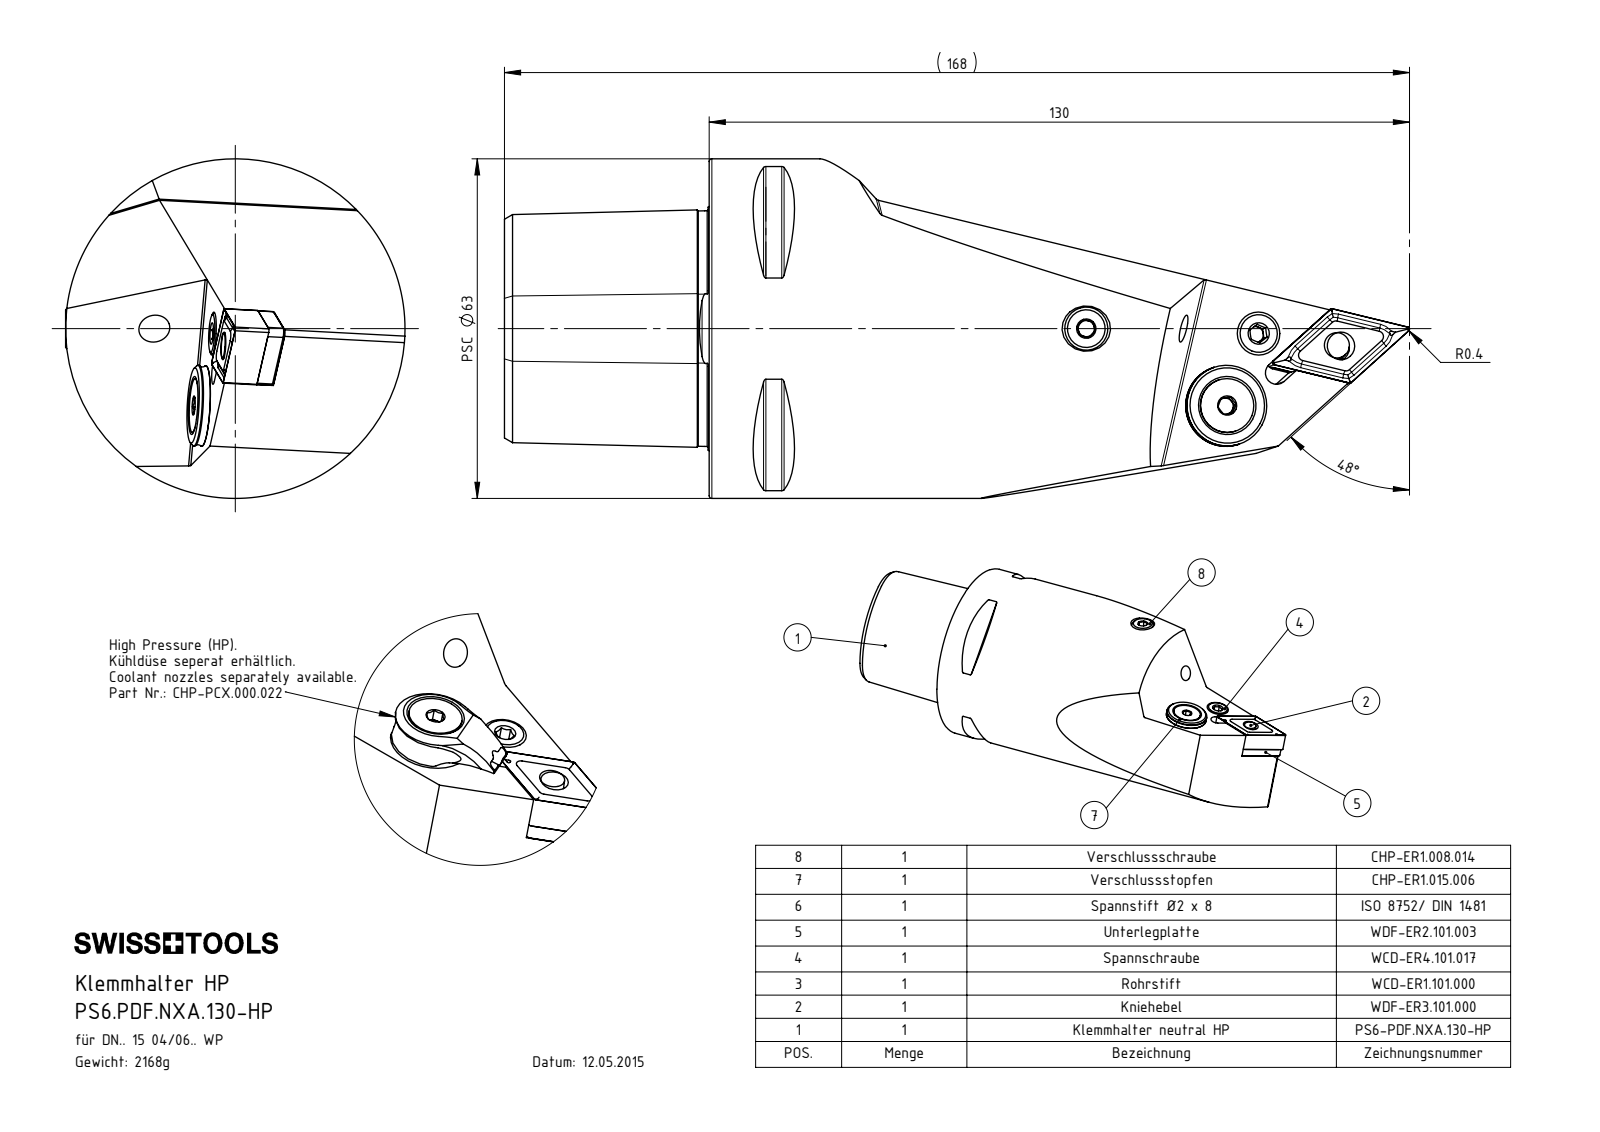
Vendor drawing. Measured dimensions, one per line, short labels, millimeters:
name: WDF-ER3.101.000_A; PS6.PDF.NXA.130-HP; DIN 7991 - M5x15; CHP-ER1.015.006_A (+8 more)
written by: SolidWorks 2017 (AUTOMOTIVE_DESIGN)
unit: mm
bodies: 11 solids, 324 faces (130 planar, 69 cylindrical, 125 other)
size: 168 × 63 × 63
volume: 277 043 mm³; area: 43 254 mm²
holes: 2× ⌀4.2, 2× ⌀5, 2× ⌀7, 1× ⌀1.2, 1× ⌀2, 1× ⌀2.5, 1× ⌀3, 1× ⌀4, 1× ⌀5.16, 1× ⌀5.2, 1× ⌀6.4, 1× ⌀8.1
bosses: 2× ⌀8, 1× ⌀63, 1× ⌀15, 1× ⌀13.4, 1× ⌀10, 1× ⌀7.9, 1× ⌀6.4, 1× ⌀5.5
rounds: 9× R0.5, 4× R0.4, 4× R1, 3× R2.5, 2× R0.8, 2× R3.2, 1× R2.1, 1× R2.35
face distances: 12.41, 38, 6.02, 24.88, 3.18, 9.2, 12.7, 4.72, 1.54, 4.48
hole spacings: 24.43, 4.5, 20.87, 20.88, 4.51, 4.52, 10.39, 10.4
